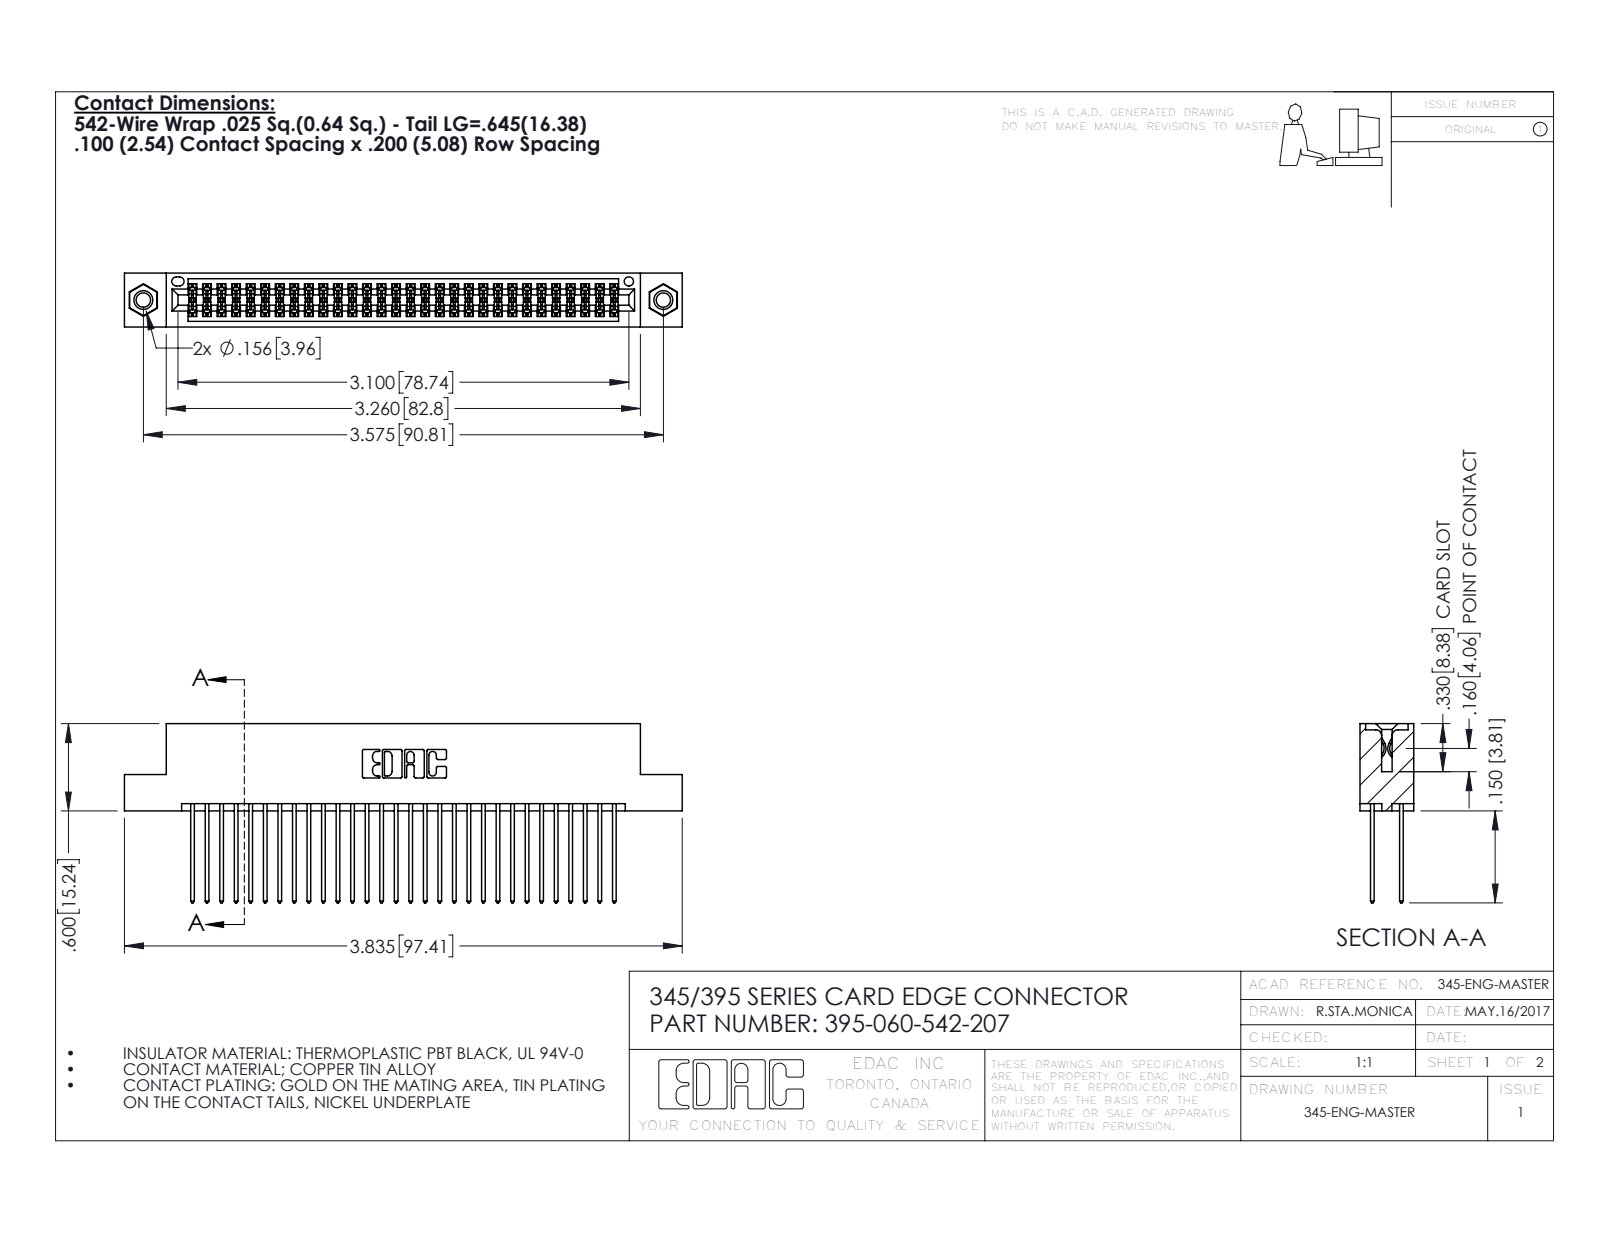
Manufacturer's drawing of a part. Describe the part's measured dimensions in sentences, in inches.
The part is named "395-060-542-207; 345-250-001_345-250-005-103; 345 Part_Flush Mounting Lugs - 0.156 Dia-TI; 345-292-001_345-293-142". Its 3-D file was written by "SolidWorks 2016 (CONFIG_CONTROL_DESIGN)". It is 63 solids with 3186 faces: 2092 planar, 1078 cylindrical and 16 other. Overall it measures 3.835 by 1.232 by 0.37 inches. Its volume is 0.587 cubic inches and its surface area 23.74 square inches. Round holes: 2 of diameter 0.098, 2 of diameter 0.125, 2 of diameter 0.156, 1 of diameter 0.064. Round bosses or shafts: 2 of diameter 0.155. Partial cylindrical surfaces (rounded edges, fillets, slot ends): 90 of radius 0.006, 60 of radius 0.01, 22 of radius 0.01, 6 of radius 0.007, 6 of radius 0.031, 3 of radius 0.026, 2 of radius 0.014, 2 of radius 0.019. The main face-to-face distances are 0.072, 0.298, 0.2, 0.098, 0.272, 0.025, 0.37, 0.225, 0.175, 0.149. The hole center spacings are 0.27, 3.34, 3.575.
